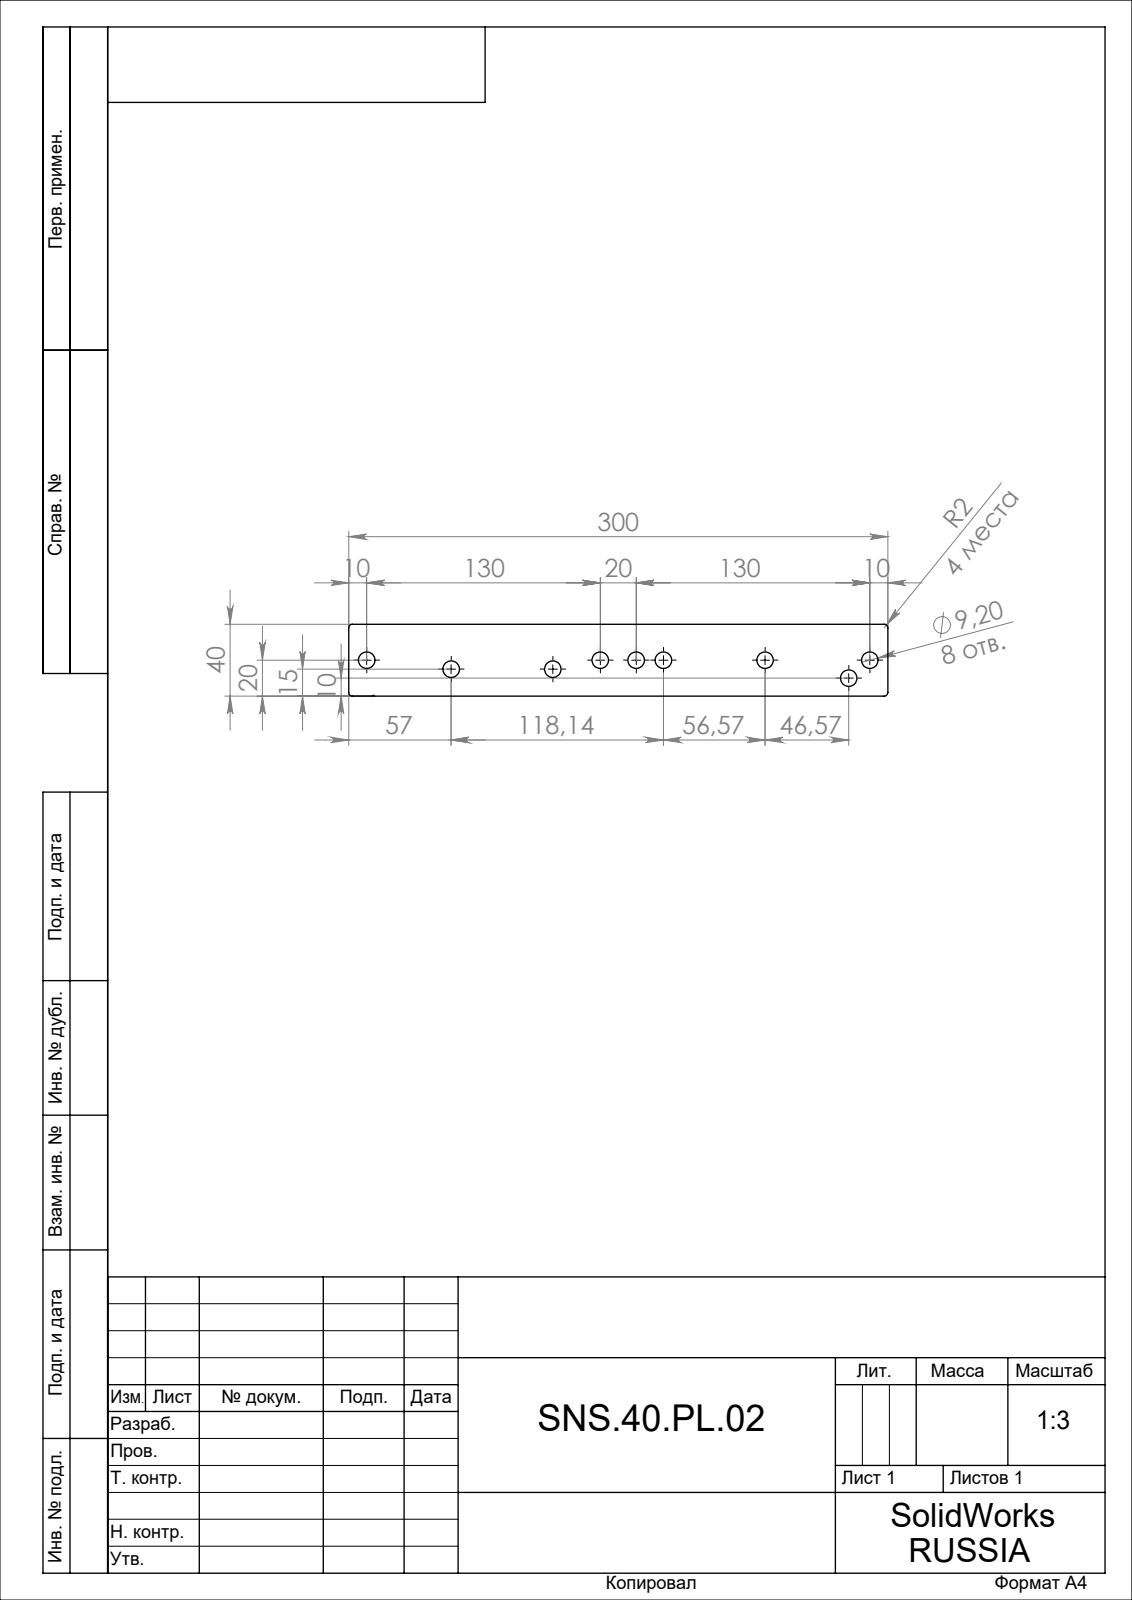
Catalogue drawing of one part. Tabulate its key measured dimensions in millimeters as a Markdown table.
| quantity | value |
| --- | --- |
| STEP written by | SolidWorks 2018 (AUTOMOTIVE_DESIGN) |
| units | millimeters |
| bodies | 1 solid, 30 faces (7 planar, 23 cylindrical, 0 other) |
| overall size | 300 × 40 × 5 |
| volume | 56 989 mm³ |
| surface area | 27 482 mm² |
| round holes (diameter × count) | 9.2 × 9 |
| partial cylindrical surfaces (radius × count) | 2 × 4, 0.5 × 1 |
| main face-to-face distances | 5, 40, 300 |
| hole center spacings | 56.57, 118.25, 130, 150, 15.14, 15.41, 20, 26.9 |
